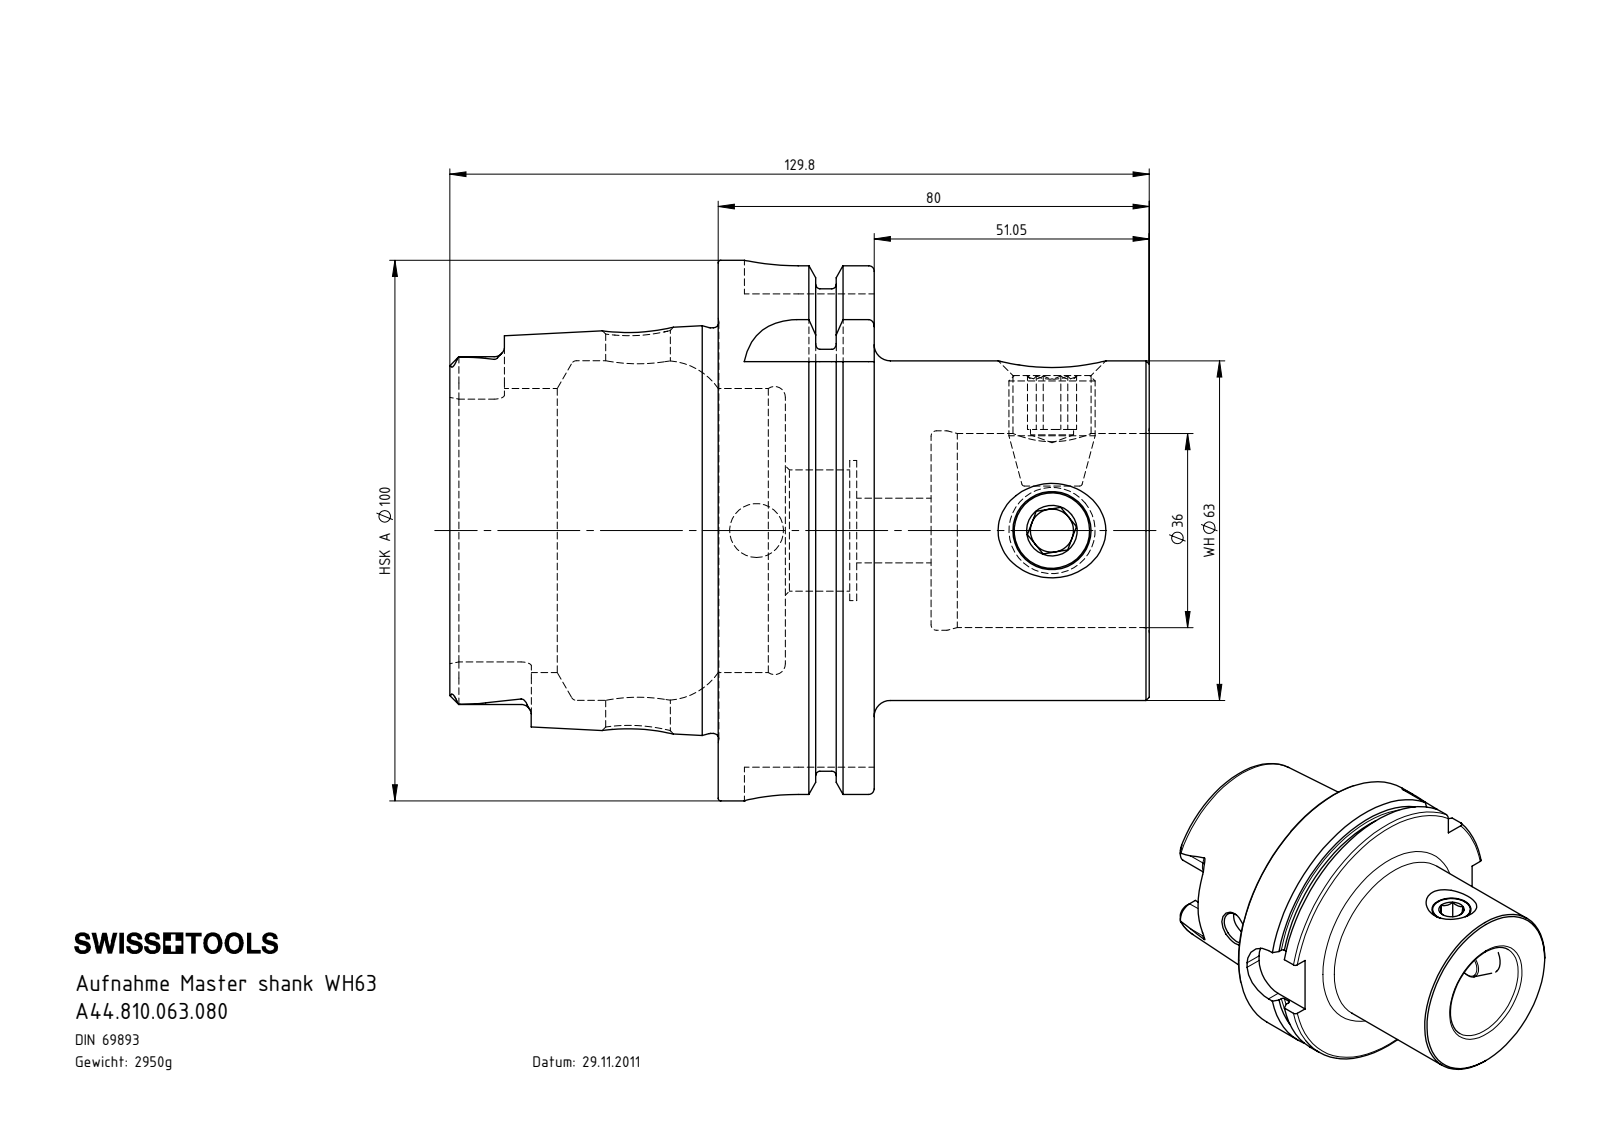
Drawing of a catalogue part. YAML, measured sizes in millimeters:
part_name: "WH6-ER1.001.021; HA0-WH6.K01.080_B_Weichbearbeitung; HA0.WH6.K01.080"
step_written_by: "SolidWorks 2017 (AUTOMOTIVE_DESIGN)"
units: millimeters
bodies: {solids: 3, faces: 172, planar: 71, cylindrical: 42, other: 59}
overall_size: [129.8, 100.3, 100.3]
volume: 375407
surface_area: 67834
round_holes:
  - {diameter: 8, count: 2}
  - {diameter: 12, count: 2}
  - {diameter: 14.5, count: 2}
  - {diameter: 10, count: 1}
  - {diameter: 22.5, count: 1}
  - {diameter: 26, count: 1}
  - {diameter: 36, count: 1}
  - {diameter: 37, count: 1}
  - {diameter: 52.7, count: 1}
  - {diameter: 63, count: 1}
round_bosses_or_shafts:
  - {diameter: 16, count: 2}
  - {diameter: 100.3, count: 1}
  - {diameter: 91.95, count: 1}
  - {diameter: 75.26, count: 1}
partial_cylinders:
  - {radius: 1.9, count: 8}
  - {radius: 4.88, count: 4}
  - {radius: 10, count: 4}
face_to_face_distances: [28.95, 80, 51.05, 12.45, 16.5, 67.55, 49.8, 62.25, 78.75, 129.8]
hole_center_spacings: [54.85, 76.85]
